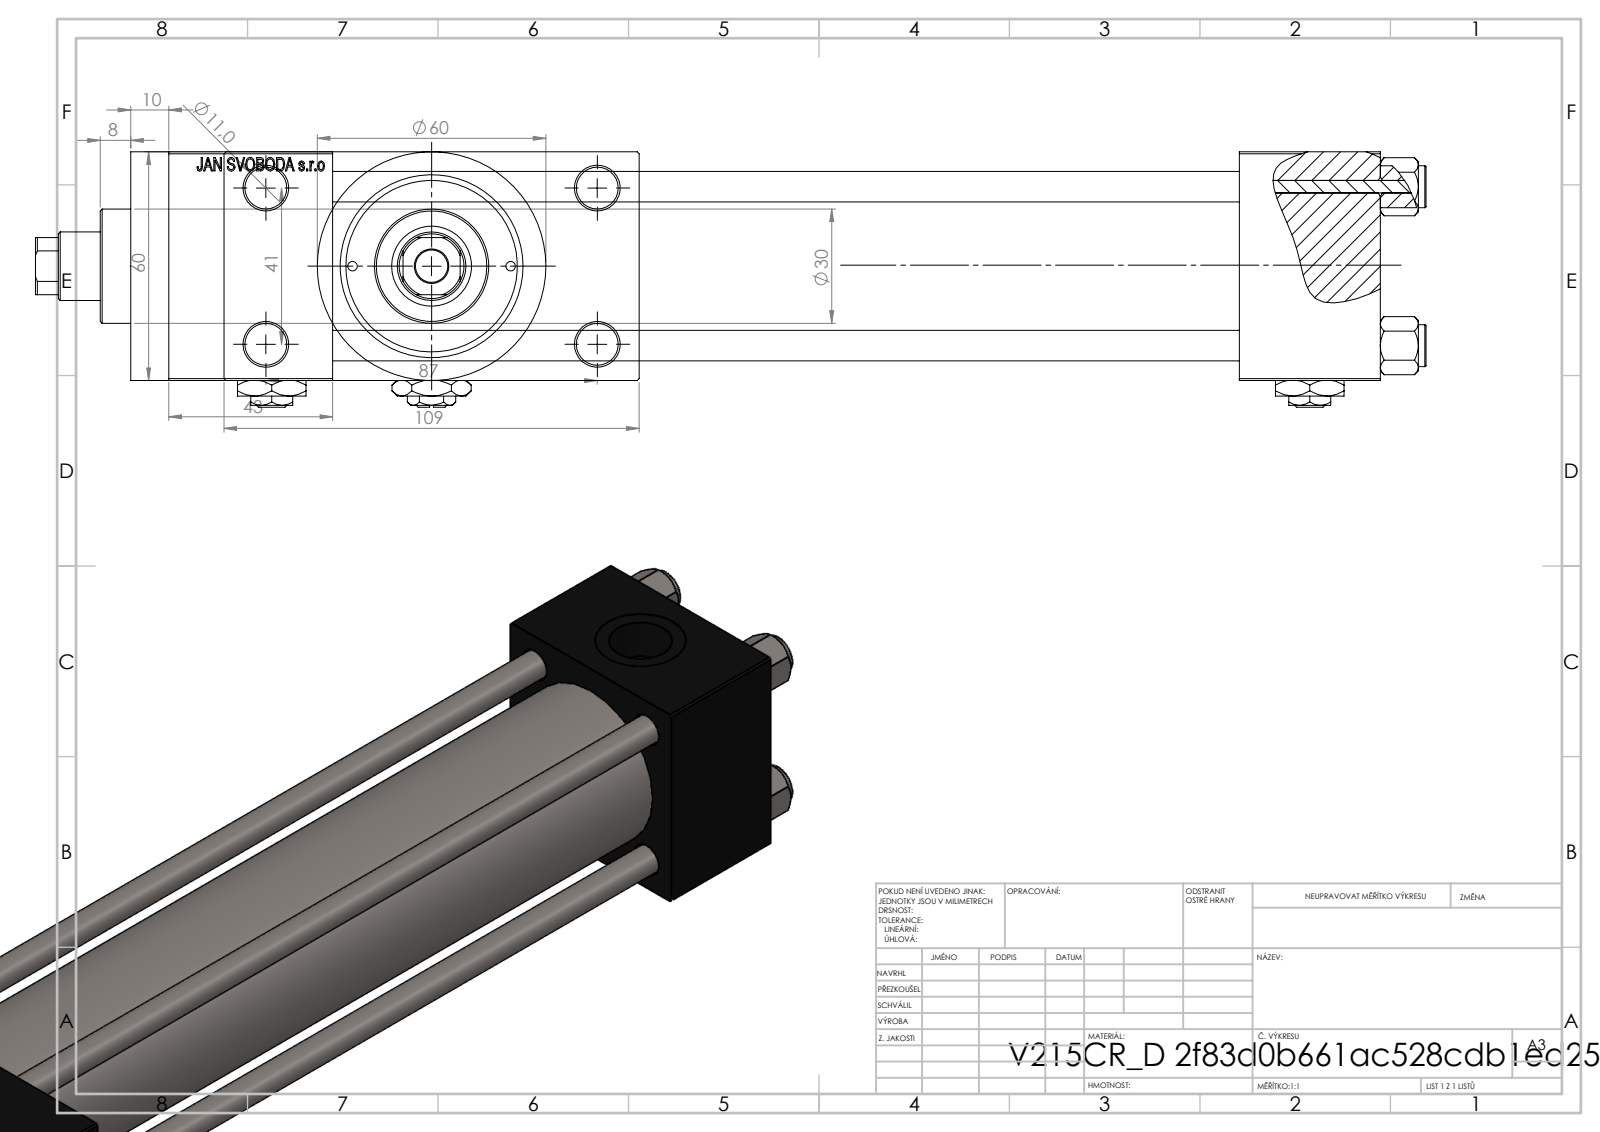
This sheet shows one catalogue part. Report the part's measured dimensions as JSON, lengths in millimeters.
{"part_name": "V215CR_D_Body; V215_VC_A; Zatka_pro_OIL_PORT; V215CR_D_TYCINKA (+2 more)", "step_written_by": "SolidWorks 2019 (CONFIG_CONTROL_DESIGN)", "units": "millimeters", "bodies": {"solids": 13, "faces": 1214, "planar": 548, "cylindrical": 104, "other": 562}, "overall_size": [365, 109, 67], "volume_mm3": 670323, "surface_area_mm2": 200779, "round_holes": [[8, 4], [11, 4], [2.5, 2], [7, 2], [16.66, 2], [24, 2], [8.5, 1], [18, 1], [21, 1], [31, 1], [40, 1], [45, 1]], "round_bosses_or_shafts": [[11, 4], [60, 1], [46, 1], [30, 1]], "partial_cylinders_radius": [[8.5, 1]], "face_to_face_distances": [60, 24.5, 84.5, 238, 37, 275, 43, 318, 281, 109], "hole_center_spacings": [20.85, 22.65, 29.49, 30.62, 41.7, 46.53, 47.15, 48.09]}
